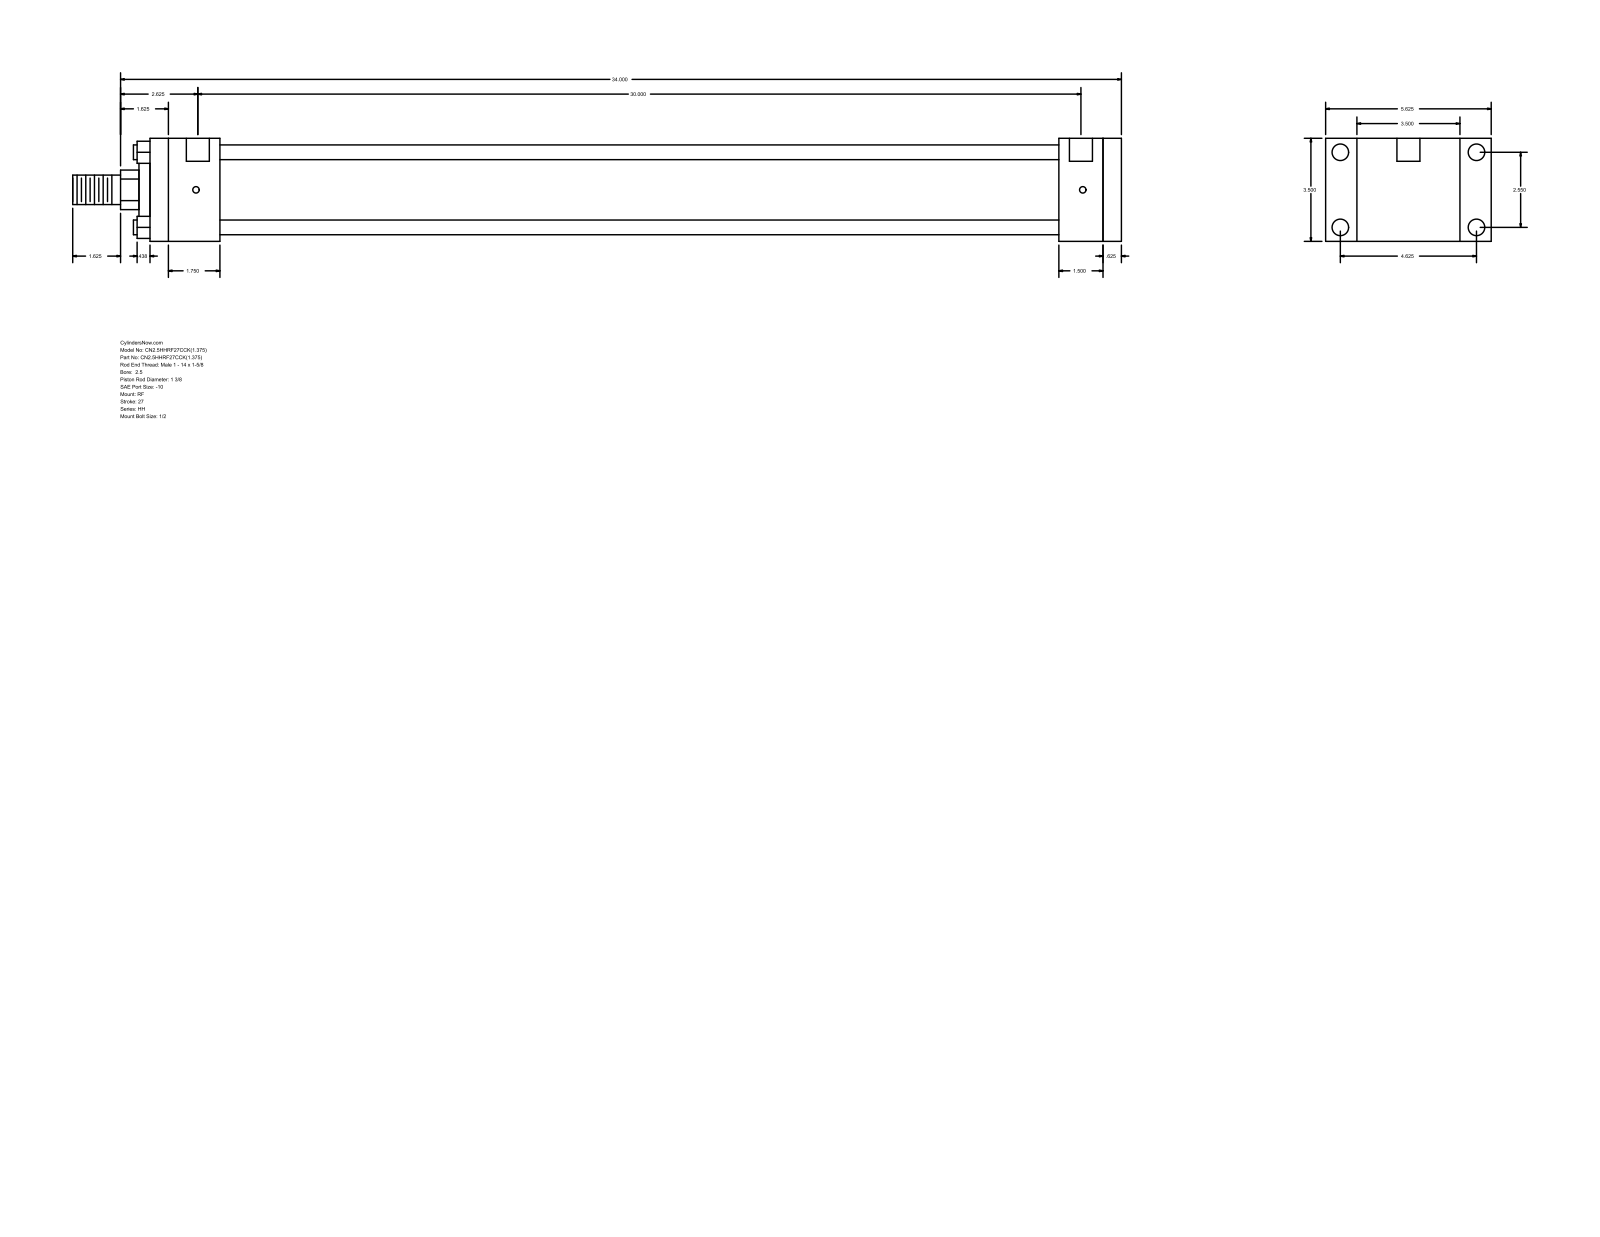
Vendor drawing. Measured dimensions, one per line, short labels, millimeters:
name: HH_RF__0250_1.375
written by: GSSL Pune (CONFIG_CONTROL_DESIGN)
unit: mm
bodies: 0 solids, 92 faces (64 planar, 28 cylindrical, 0 other)
size: 904.88 × 142.88 × 88.9
holes: 4× ⌀5.56, 4× ⌀14.3, 2× ⌀19.84
bosses: 4× ⌀12.7, 1× ⌀73.03, 1× ⌀50.8, 1× ⌀34.92, 1× ⌀25.4
rounds: 1× R17.06
face distances: 88.9, 838.2, 822.33, 15.87, 60.32, 762.01, 777.88, 784.22, 723.9, 38.11
hole spacings: 64.76, 117.48, 134.15, 765.17, 1.58, 1.59, 762, 763.58
